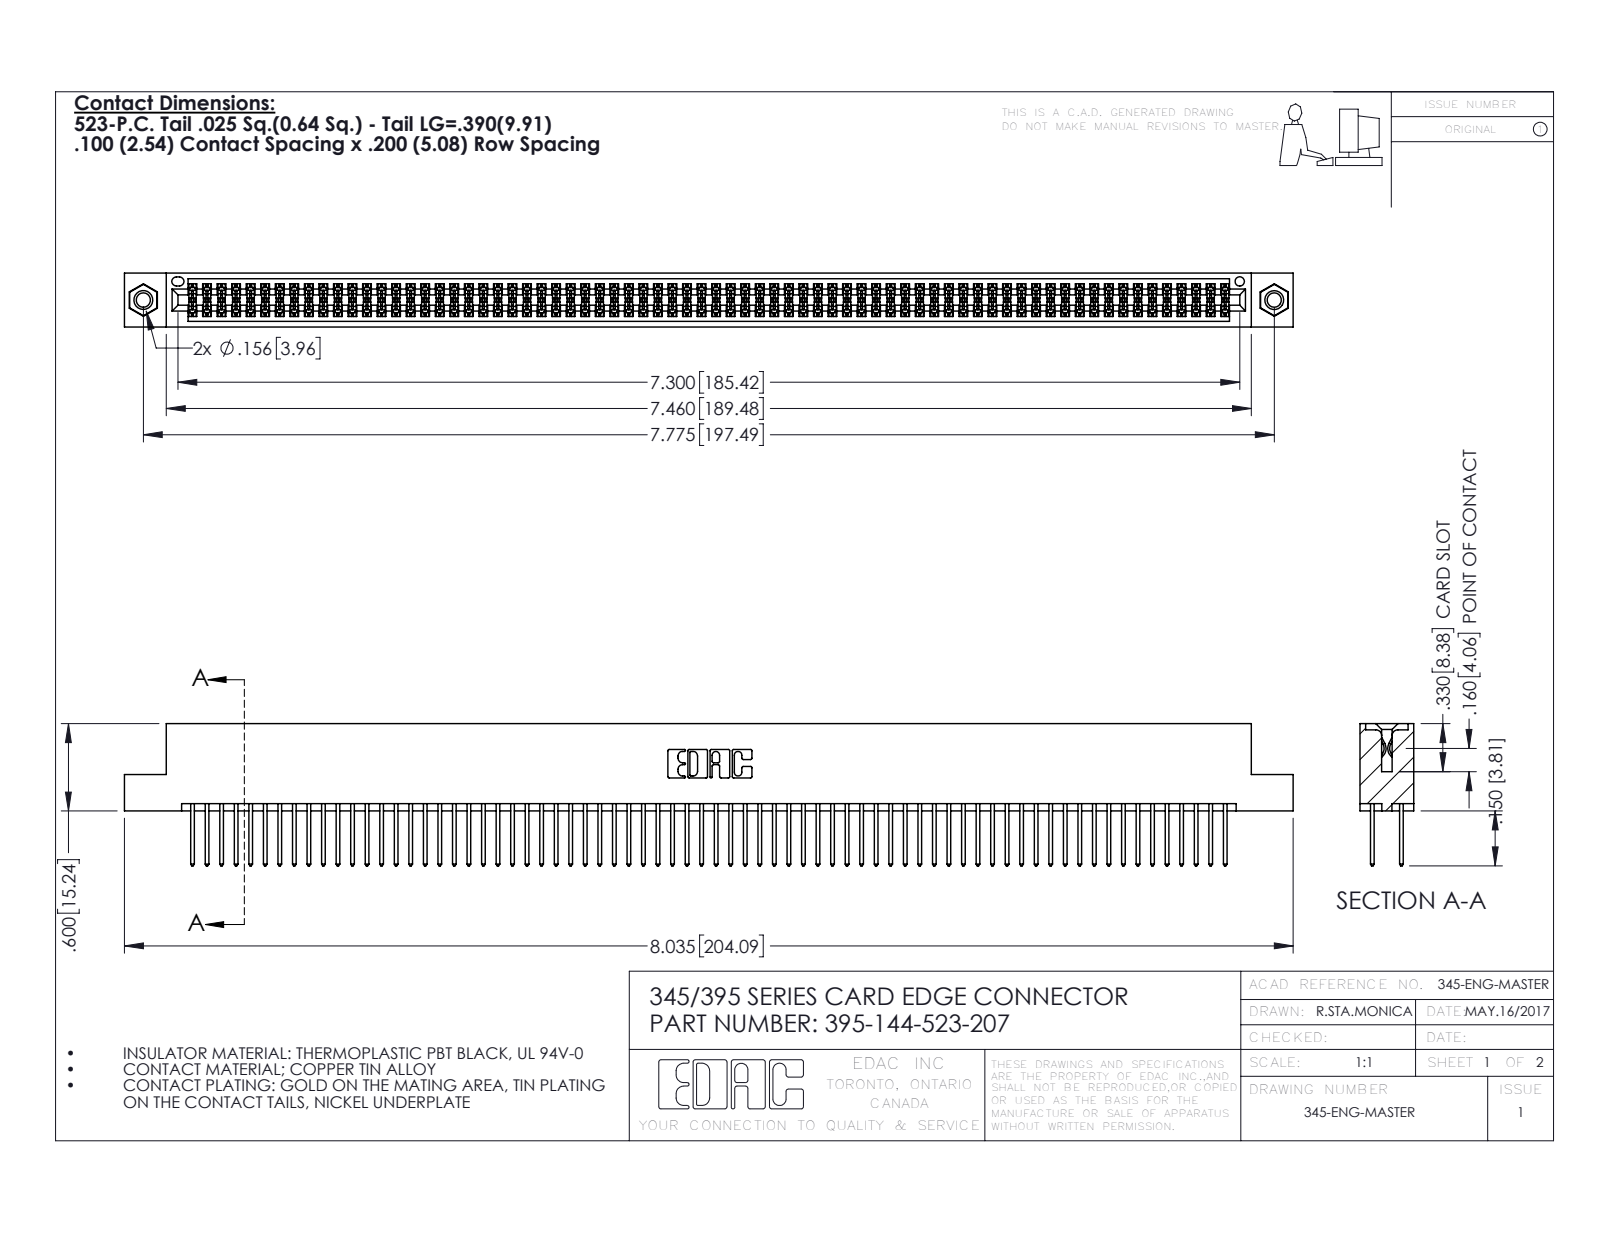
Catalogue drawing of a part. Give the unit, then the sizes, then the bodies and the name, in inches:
Units: inches
Overall size (bounding box): 8.035 × 0.977 × 0.37
Round holes (diameter × count): ⌀0.098 ×2, ⌀0.125 ×2, ⌀0.156 ×2, ⌀0.064 ×1
Round bosses / shafts (diameter × count): ⌀0.155 ×2
Partial cylindrical surfaces — rounded edges, fillets, slot ends (radius × count): R0.006 ×216, R0.01 ×144, R0.01 ×22, R0.007 ×6, R0.031 ×6, R0.026 ×3, R0.014 ×2, R0.019 ×2
Main face-to-face distances: 0.072, 0.298, 0.2, 0.098, 0.272, 0.025, 0.37, 0.225, 0.175, 0.149
Hole centre spacings: 0.27, 7.539, 7.775
Volume: 1.244 in³ · Surface area: 49.7 in²
Bodies: 147 solids, 7386 faces (4864 planar, 2506 cylindrical, 16 other)
Part name (STEP PRODUCT): 395-144-523-207; 345-292-001_345-293-123; 345 Part_Flush Mounting Lugs - 0.156 Dia-TI; 345-250-001_345-250-005-103
STEP written by: SolidWorks 2016 (CONFIG_CONTROL_DESIGN)
